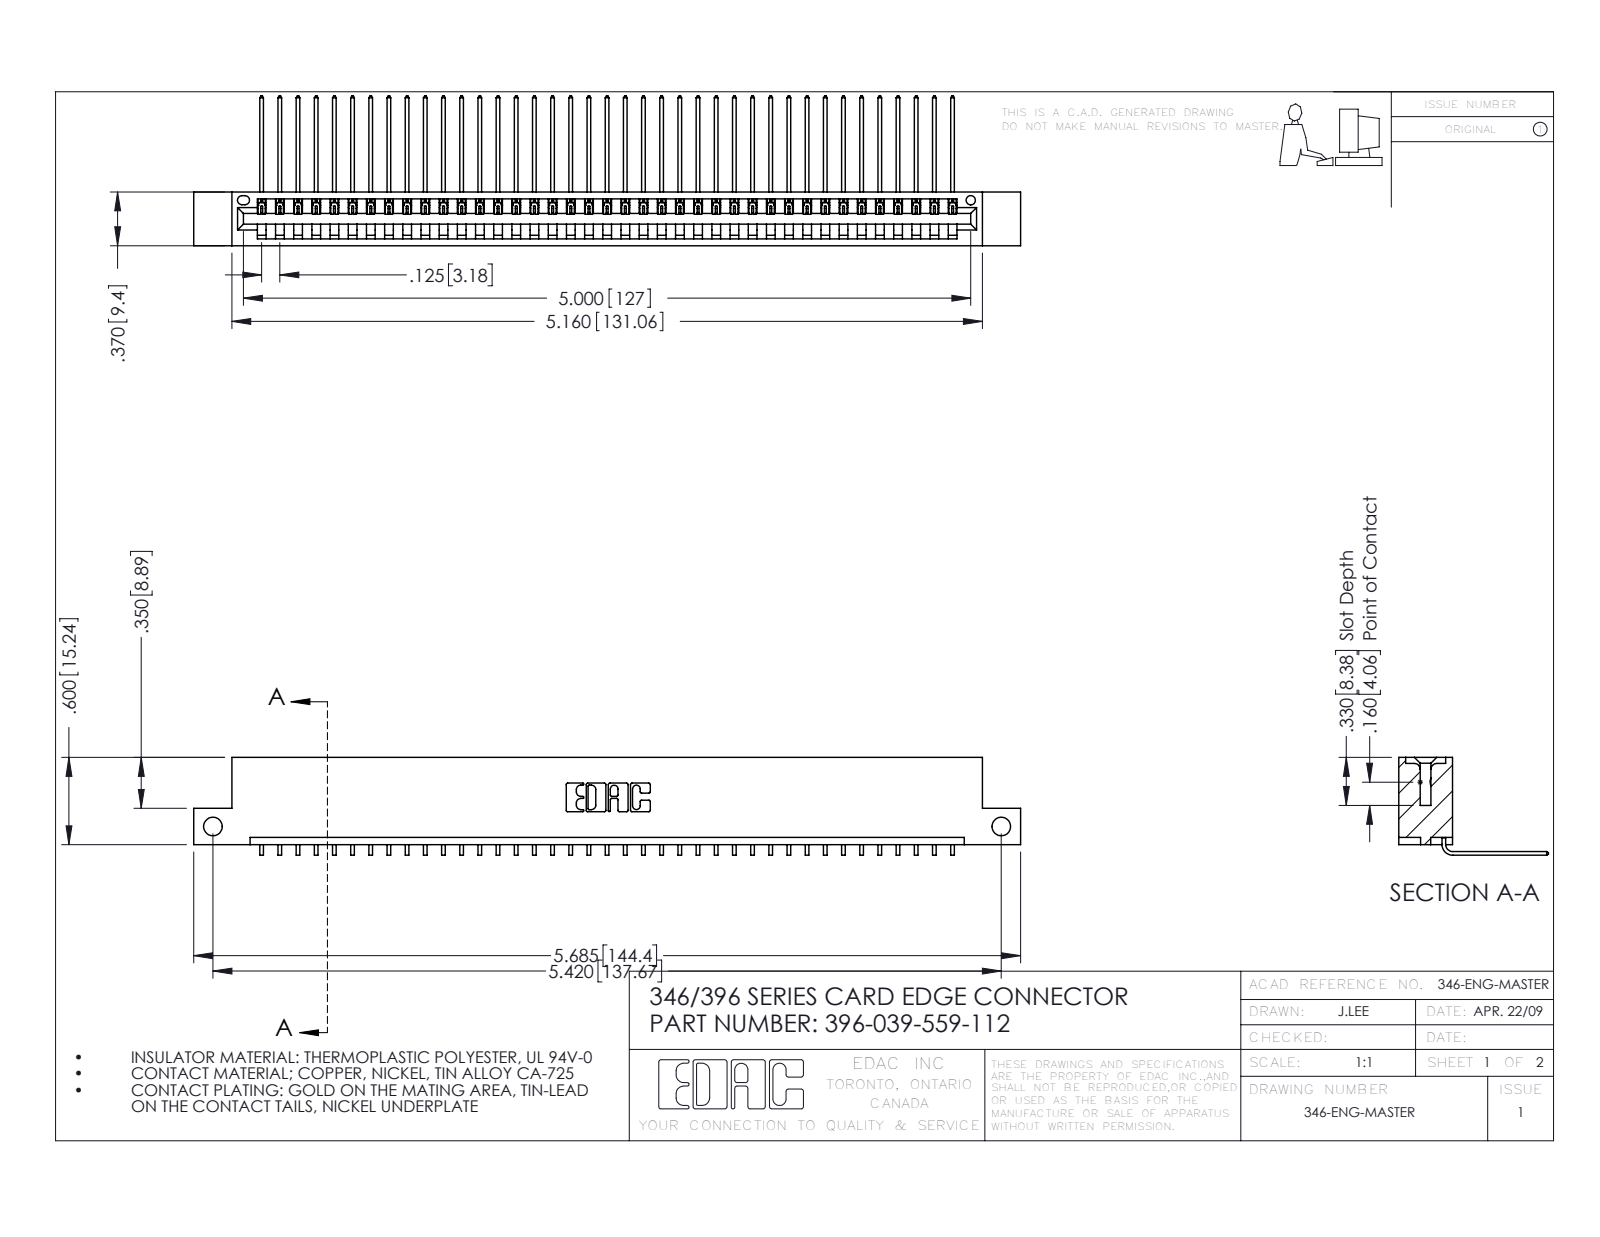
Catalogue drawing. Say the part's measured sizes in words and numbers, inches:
The part is named "396-039-559-112; 345-292-001_558 559 Tail - 1; 346 Part_Flush Mounting Lugs - Side Mount". Its 3-D file was written by "SolidWorks 2016 (CONFIG_CONTROL_DESIGN)". It is 40 solids with 2462 faces: 1714 planar, 748 cylindrical and 0 other. Overall it measures 5.685 by 1.03 by 0.673 inches. Its volume is 0.845 cubic inches and its surface area 27.75 square inches. Round holes: 2 of diameter 0.128, 1 of diameter 0.064. Partial cylindrical surfaces (rounded edges, fillets, slot ends): 78 of radius 0.006, 22 of radius 0.01, 6 of radius 0.007, 6 of radius 0.031, 3 of radius 0.026, 2 of radius 0.031, 2 of radius 0.04, 1 of radius 0.014. The main face-to-face distances are 0.048, 0.322, 0.37, 0.25, 0.072, 0.025, 0.298, 0.148, 0.222, 0.1. The hole center spacings are 5.42.
